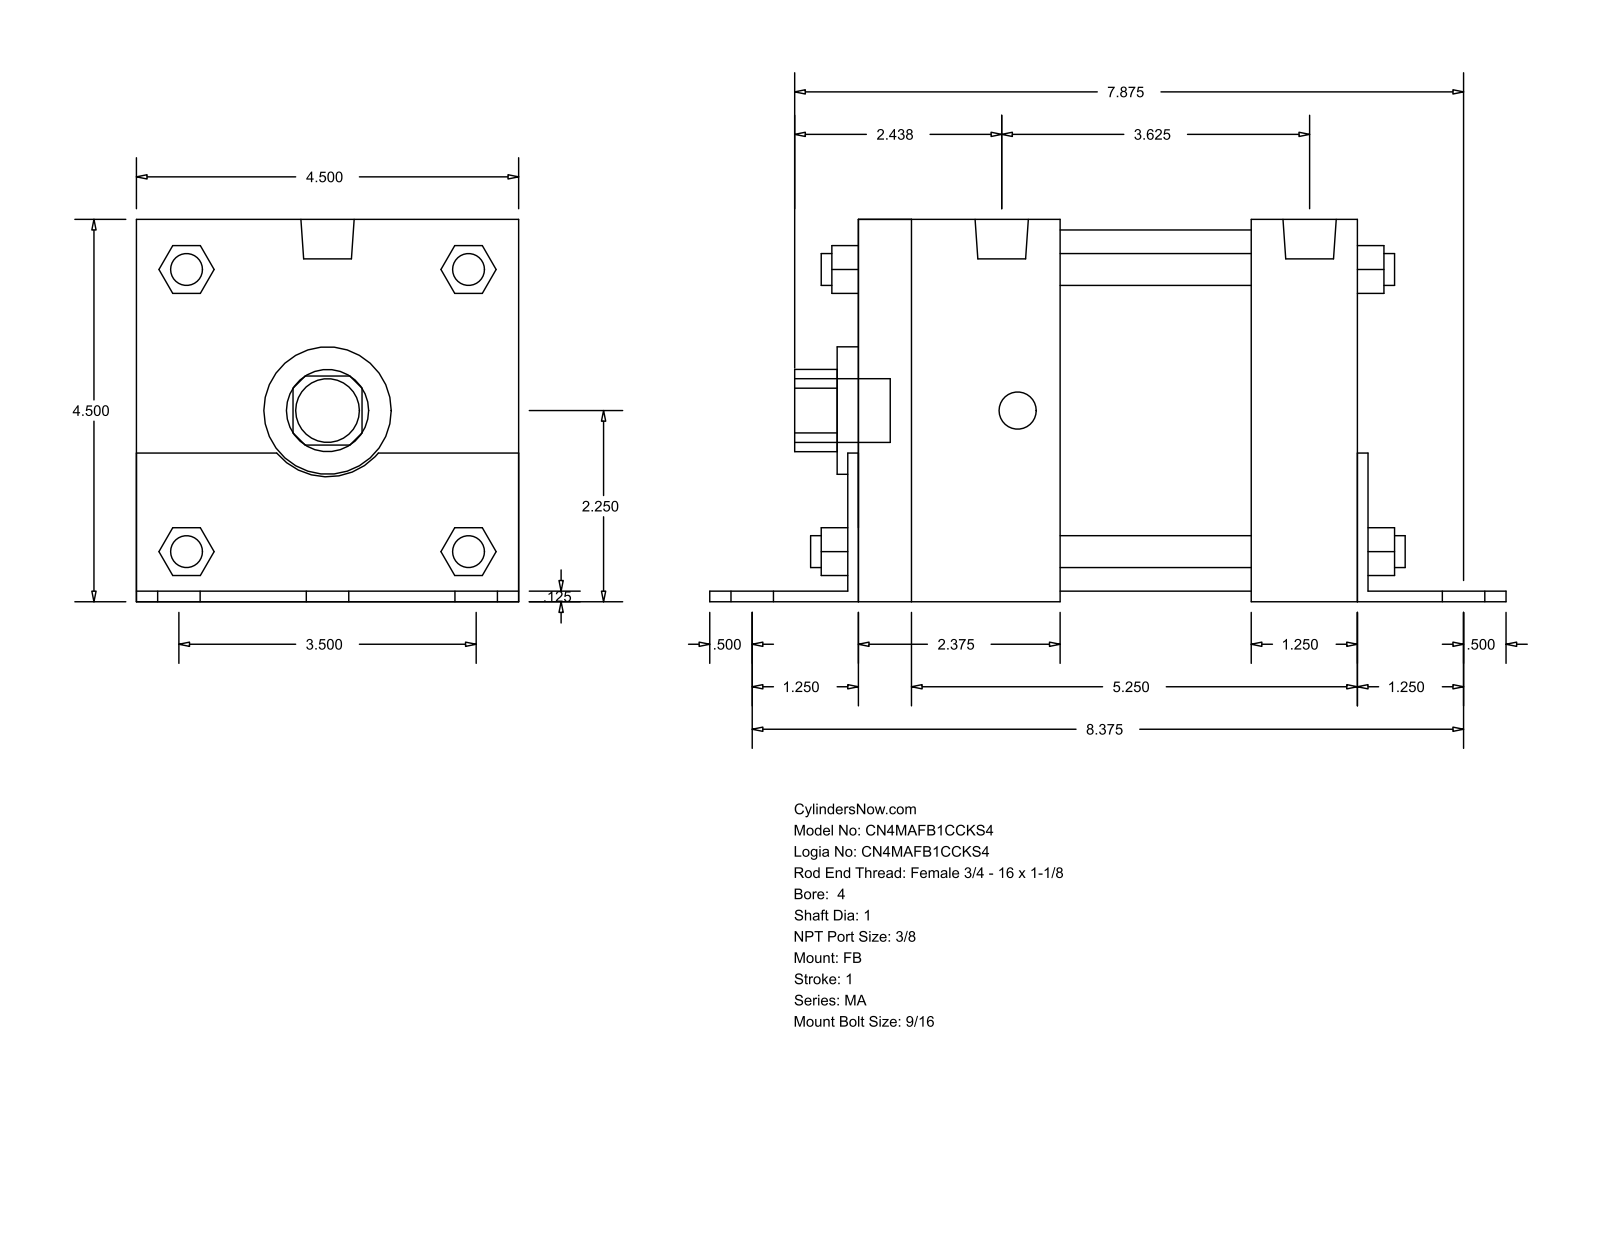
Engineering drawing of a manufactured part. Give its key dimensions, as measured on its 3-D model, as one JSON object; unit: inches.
{"part_name": "MA_FB__0400_1", "step_written_by": "GSSL Pune (CONFIG_CONTROL_DESIGN)", "units": "inches", "bodies": {"solids": 0, "faces": 140, "planar": 105, "cylindrical": 35, "other": 0}, "overall_size": [9.375, 4.502, 4.5], "round_holes": [[1, 1], [1.5, 1], [4.25, 1]], "round_bosses_or_shafts": [[0.563, 6], [0.437, 4], [0.375, 4], [0.627, 2], [0.75, 1]], "partial_cylinders_radius": [[0.484, 1], [0.78, 1]], "face_to_face_distances": [4.5, 0.125, 4.502, 6, 0.123, 4.377, 5.875, 6.125, 4.75, 4.625]}
